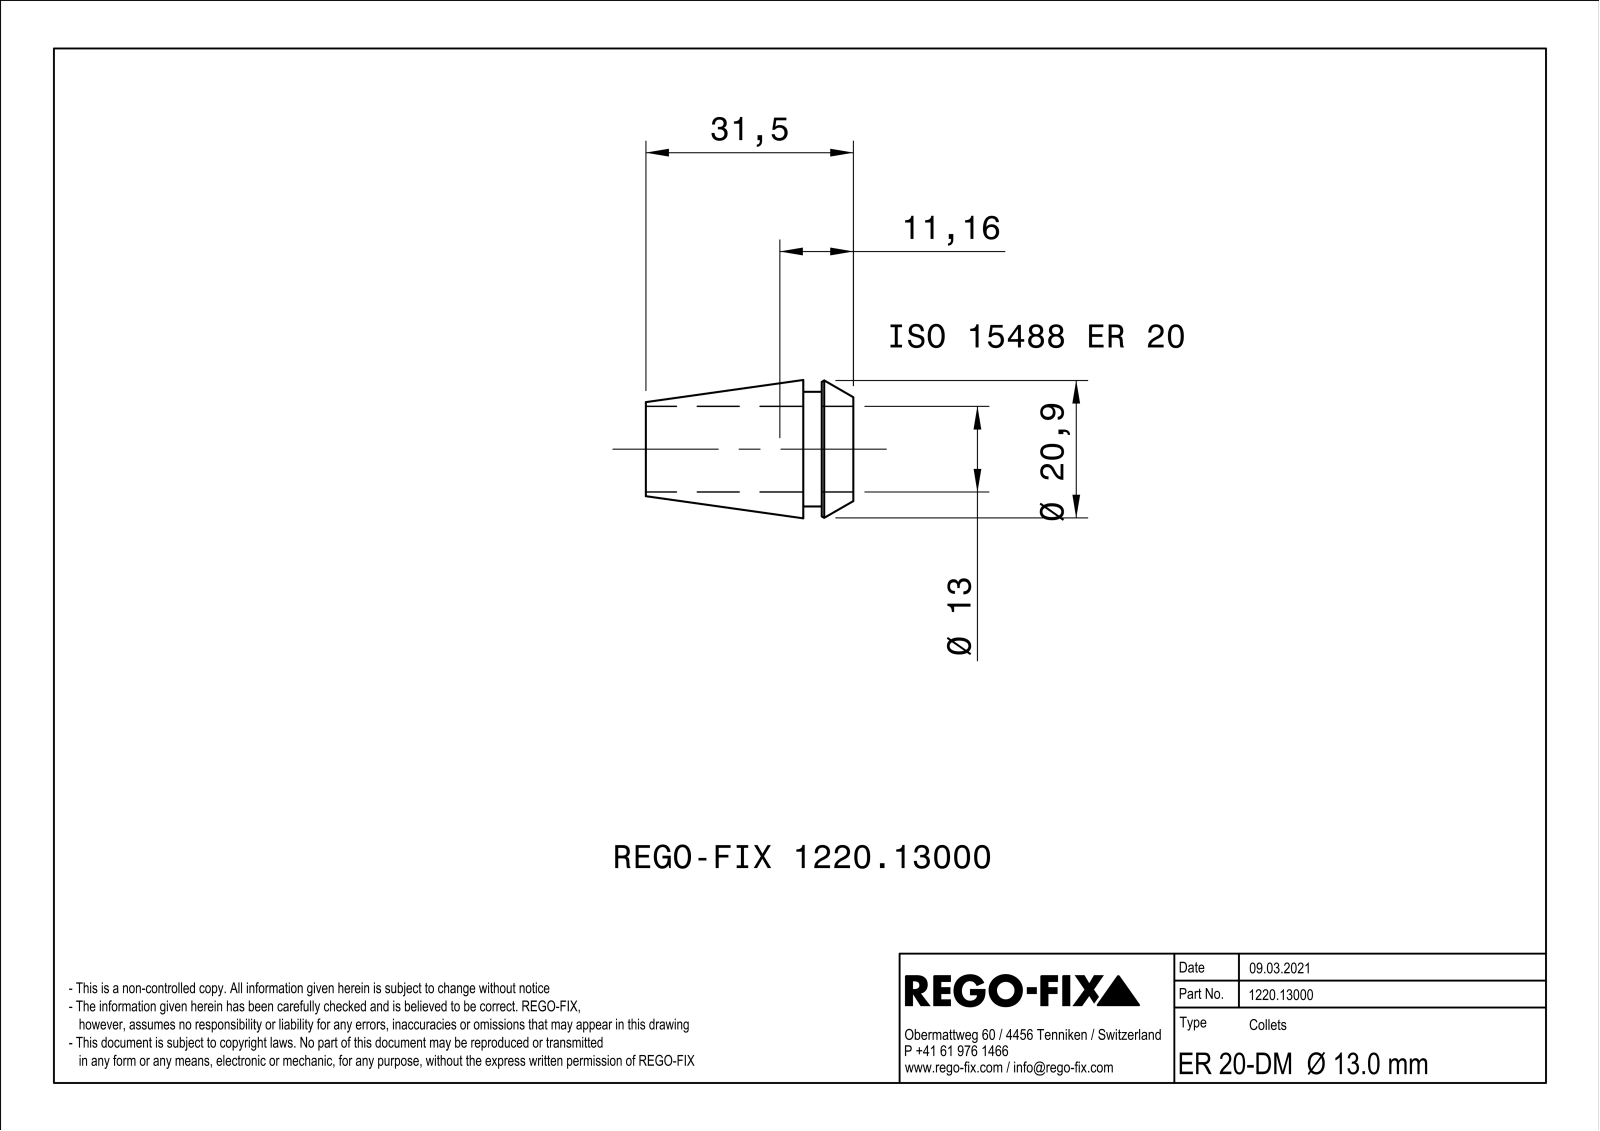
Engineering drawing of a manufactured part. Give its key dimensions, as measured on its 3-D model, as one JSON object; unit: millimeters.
{"part_name": "NOCUT", "step_written_by": "SIEMENS PLM Software Solid Edge ST10 (AUTOMOTIVE_DESIGN)", "units": "millimeters", "bodies": {"solids": 1, "faces": 154, "planar": 80, "cylindrical": 9, "other": 65}, "overall_size": [31.5, 20.98, 20.98], "volume_mm3": 3038, "surface_area_mm2": 4436, "round_holes": [[13, 1]], "round_bosses_or_shafts": [[17.4, 1]], "face_to_face_distances": [0.8, 2.8, 4.8, 7.6, 14, 9.2, 6.4, 26.5, 21.7, 18.9]}
